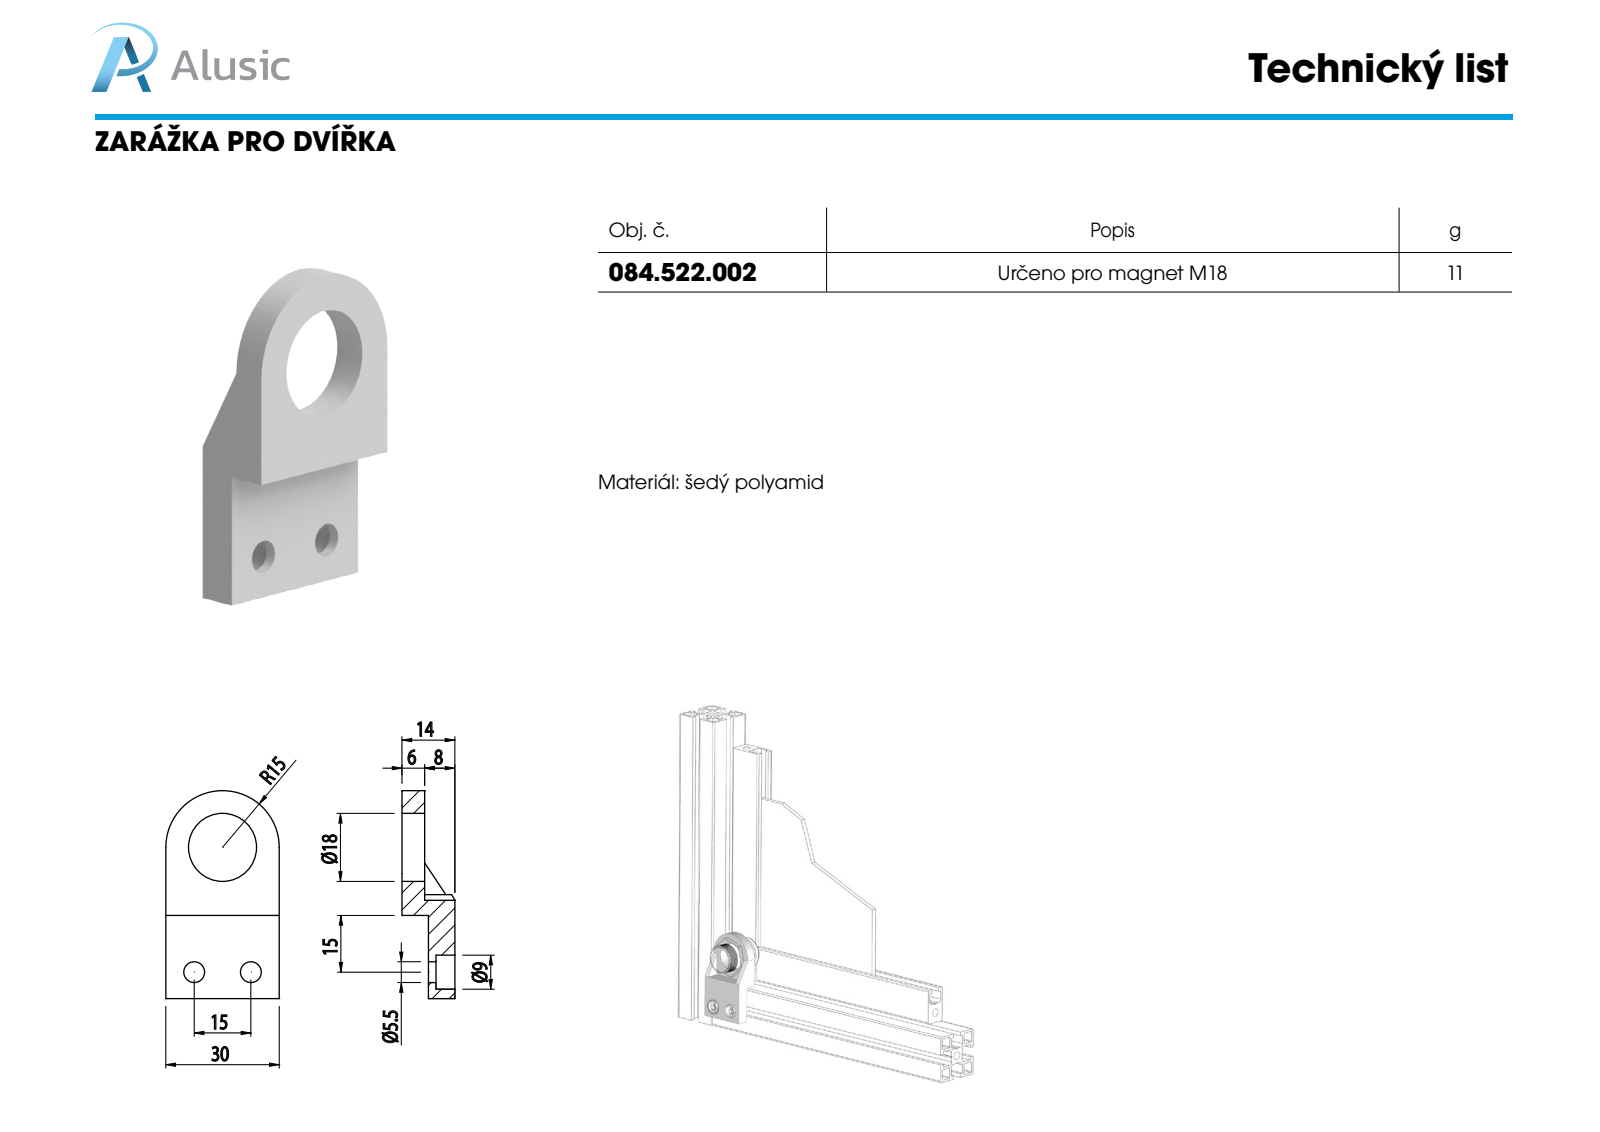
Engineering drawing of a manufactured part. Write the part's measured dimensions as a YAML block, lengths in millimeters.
part_name: "084.522.002"
step_written_by: "SolidWorks 2011 (CONFIG_CONTROL_DESIGN)"
units: millimeters
bodies: {solids: 1, faces: 26, planar: 15, cylindrical: 11, other: 0}
overall_size: [55, 30, 14]
volume: 9019
surface_area: 4914
round_holes:
  - {diameter: 5.5, count: 2}
  - {diameter: 9, count: 2}
  - {diameter: 18, count: 1}
partial_cylinders:
  - {radius: 15, count: 1}
face_to_face_distances: [7, 14, 8, 1, 6, 30, 22, 26, 4, 3]
hole_center_spacings: [33.84, 15]
